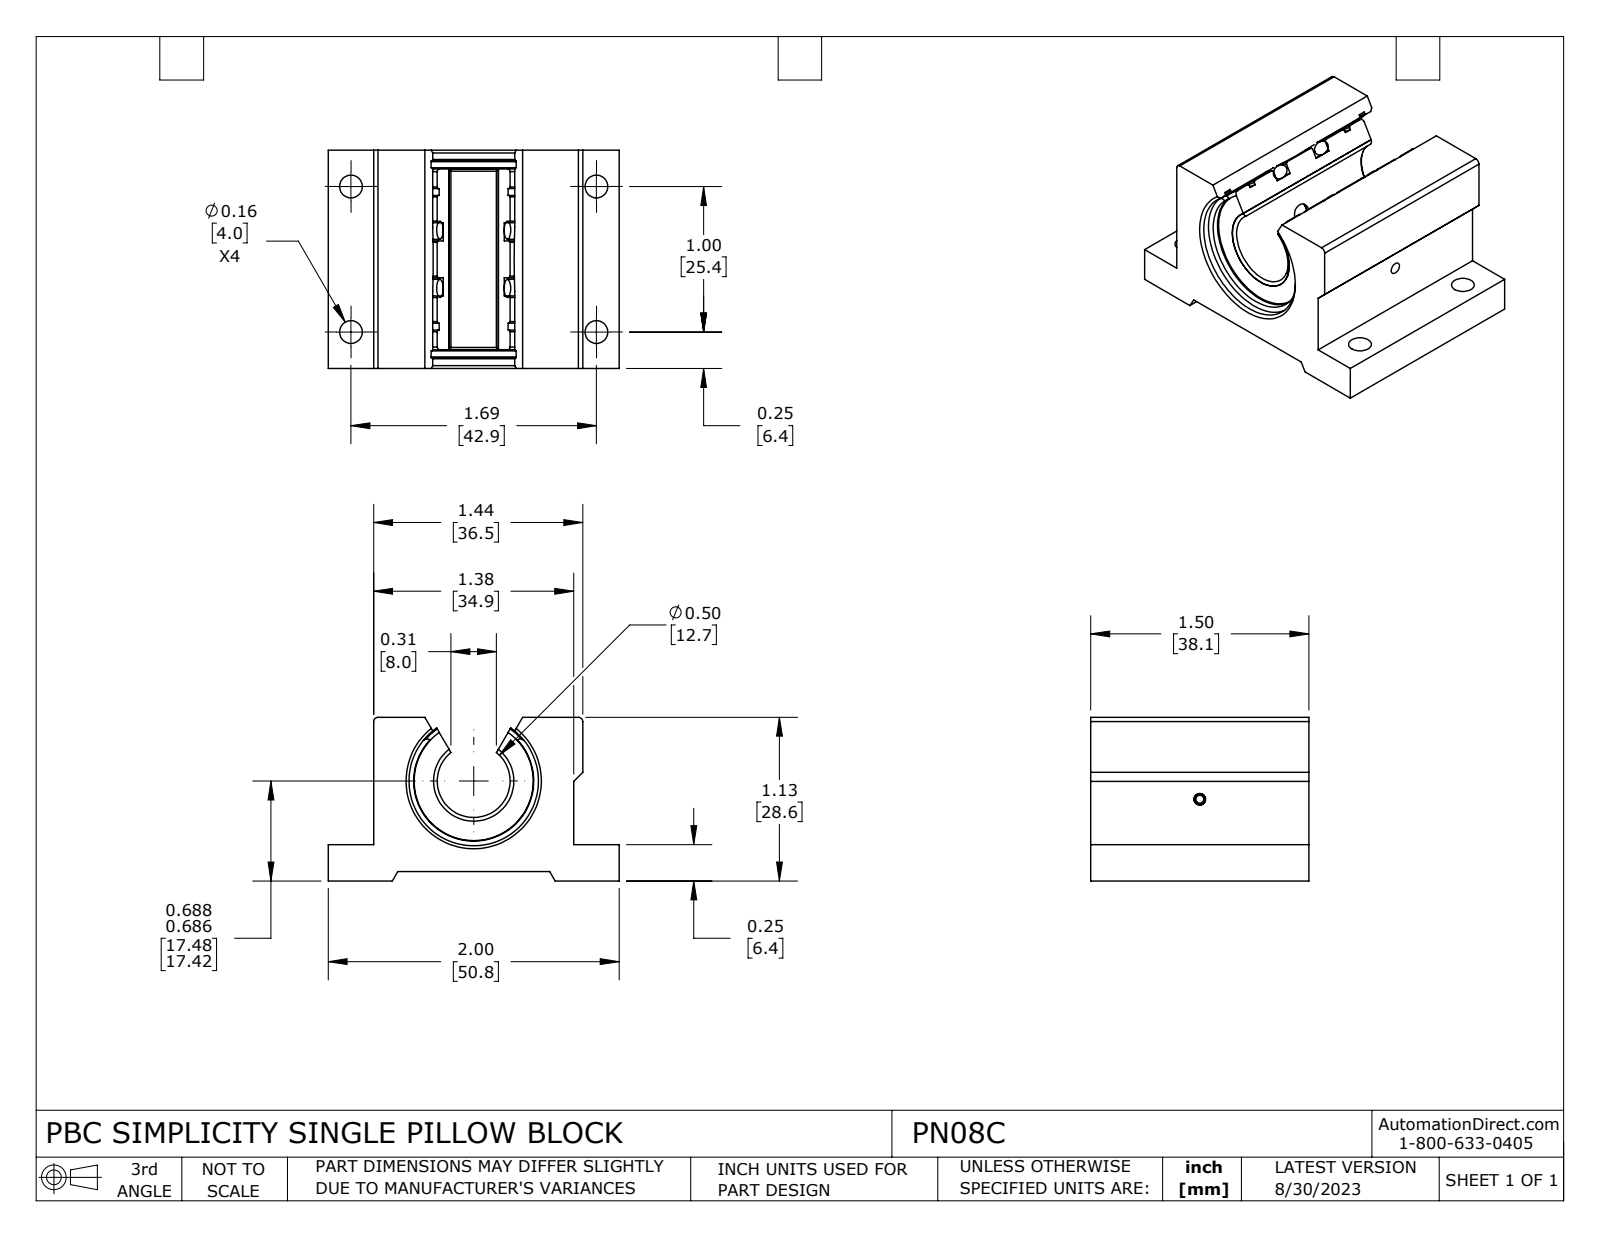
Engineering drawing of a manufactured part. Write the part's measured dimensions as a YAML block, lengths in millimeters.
part_name: "PN08C"
step_written_by: "SolidWorks 2021 (CONFIG_CONTROL_DESIGN)"
units: millimeters
bodies: {solids: 8, faces: 202, planar: 49, cylindrical: 94, other: 59}
overall_size: [50.8, 38.1, 28.6]
volume: 31120
surface_area: 17050
round_holes:
  - {diameter: 4, count: 4}
  - {diameter: 1.4, count: 1}
  - {diameter: 2, count: 1}
  - {diameter: 3.5, count: 1}
round_bosses_or_shafts:
  - {diameter: 22.2, count: 1}
  - {diameter: 20.8, count: 1}
  - {diameter: 18.1, count: 1}
  - {diameter: 2, count: 1}
partial_cylinders:
  - {radius: 0.8, count: 4}
  - {radius: 3, count: 2}
  - {radius: 6.4, count: 1}
  - {radius: 7, count: 1}
  - {radius: 10.5, count: 1}
  - {radius: 11.3, count: 1}
  - {radius: 11.8, count: 1}
  - {radius: 12.1, count: 1}
face_to_face_distances: [1.7, 6.4, 26.9, 28.6, 38.1, 4.7, 22.2, 8, 42.8, 34.9]
hole_center_spacings: [25.4, 42.8, 49.8]
